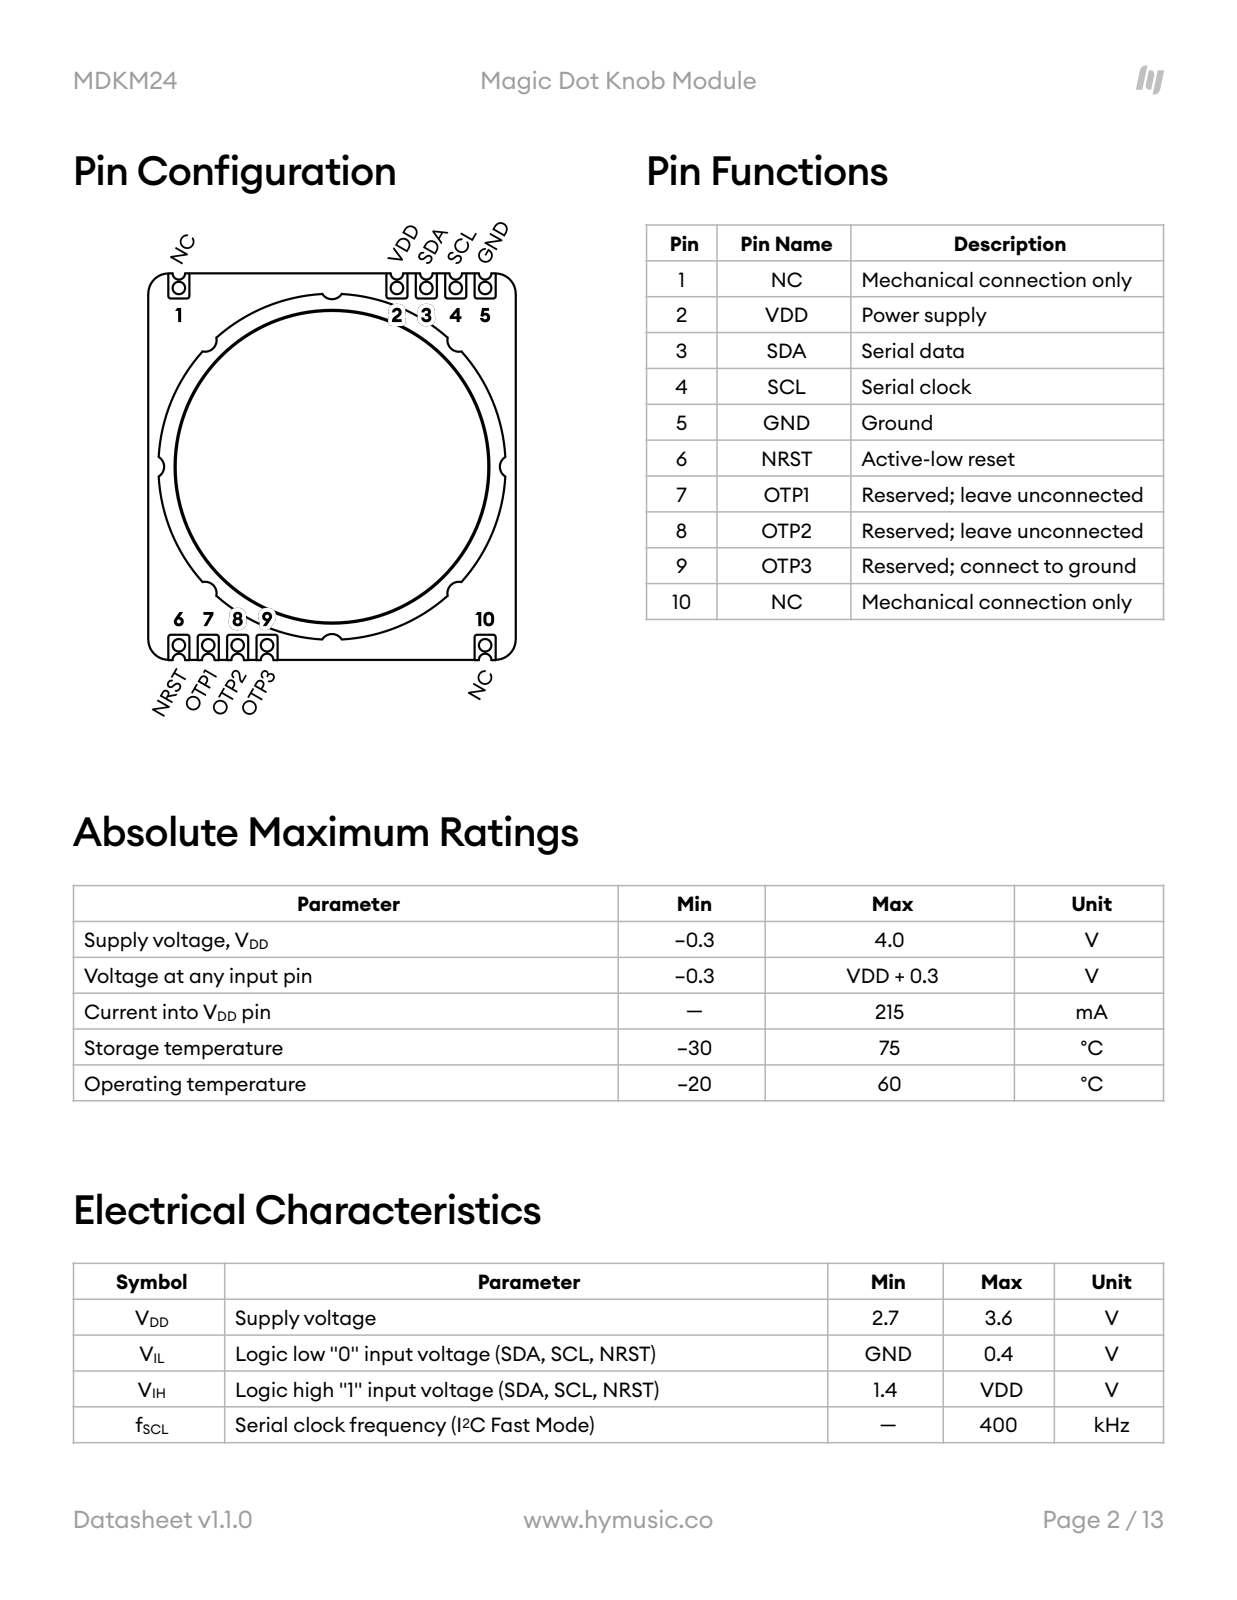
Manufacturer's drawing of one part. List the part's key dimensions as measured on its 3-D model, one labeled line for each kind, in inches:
Part name (STEP PRODUCT): Castellated Connectors; root
STEP written by: Shapr3D (AP242_MANAGED_MODEL_BASED_3D_ENGINEERING_MIM_LF)
Units: inches
Bodies: 34 solids, 1758 faces (1134 planar, 475 cylindrical, 149 other)
Overall size (bounding box): 1.32 × 1.297 × 1.25
Volume: 1.075 in³ · Surface area: 21.73 in²
Round holes (diameter × count): ⌀0.043 ×10, ⌀0.043 ×10, ⌀0.047 ×10, ⌀0.08 ×4, ⌀0.013 ×1, ⌀0.119 ×1, ⌀0.141 ×1, ⌀0.151 ×1, ⌀0.244 ×1, ⌀0.251 ×1, ⌀0.26 ×1, ⌀0.358 ×1
Round bosses / shafts (diameter × count): ⌀0.078 ×4, ⌀1.181 ×1, ⌀1.063 ×1, ⌀0.782 ×1, ⌀0.578 ×1, ⌀0.25 ×1
Partial cylindrical surfaces — rounded edges, fillets, slot ends (radius × count): R0.01 ×24, R0.017 ×22, R0.008 ×20, R0.035 ×20, R0.045 ×20, R0.05 ×20, R0.02 ×15, R0.021 ×10
Main face-to-face distances: 0.063, 0.187, 0.25, 0.962, 0.899, 0.712, 0.276, 0.276, 0.526, 0.339
Hole centre spacings: 0.2, 0.1, 0.51, 1.005, 1.02, 1, 0.1, 0.219
